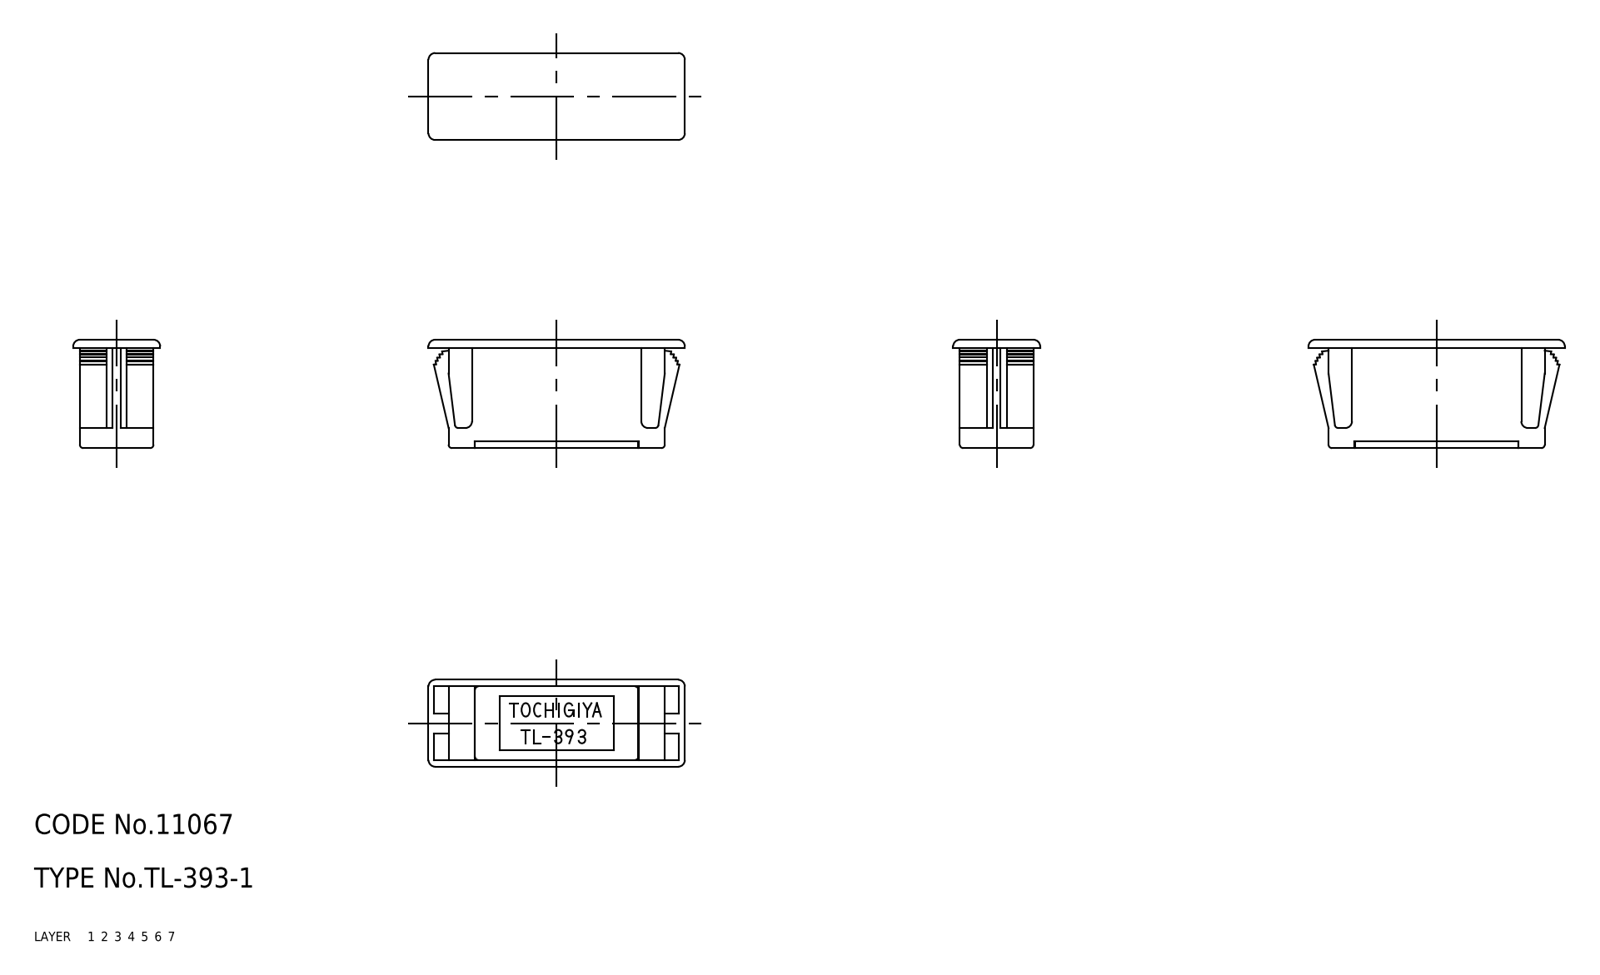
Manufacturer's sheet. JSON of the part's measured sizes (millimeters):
{"part_name": "67112870; 67112883", "step_written_by": "CADfix (AUTOMOTIVE_DESIGN)", "units": "millimeters", "bodies": {"solids": 2, "faces": 120, "planar": 0, "cylindrical": 0, "other": 120}, "overall_size": [38.3, 16.2, 13], "volume_mm3": 5295, "surface_area_mm2": 3633}
